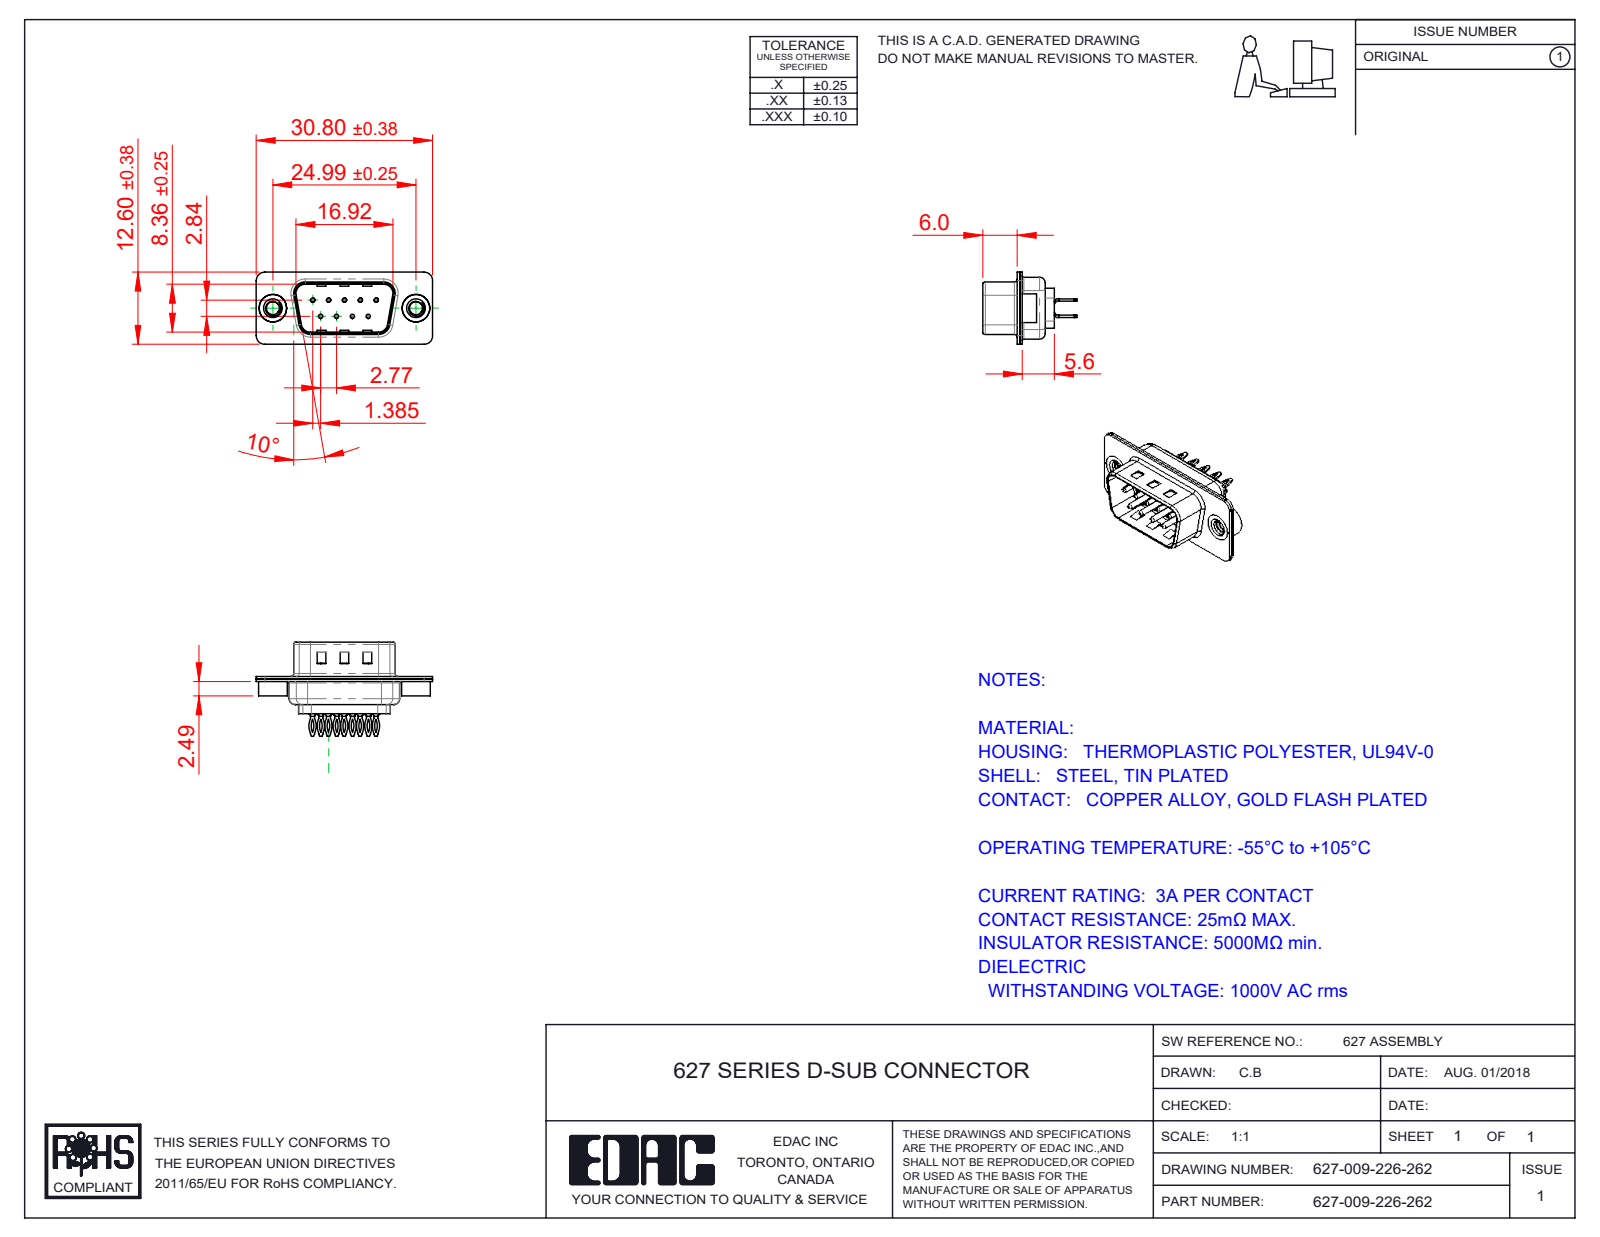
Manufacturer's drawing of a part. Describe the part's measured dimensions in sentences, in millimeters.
The part is named "627 Contact Row 2_26L; 627 Housing_09 LP; 627 Shell Front_09 Contacts; 627 Shell Rear_09 Contacts (+3 more)". Its 3-D file was written by "SolidWorks 2020 (CONFIG_CONTROL_DESIGN)". It is 14 solids with 984 faces: 287 planar, 406 cylindrical and 291 other. Overall it measures 30.8 by 16.45 by 12.6 millimeters. Its volume is 1 307 cubic millimeters and its surface area 3 895 square millimeters. Round holes: 9 of diameter 0.35, 9 of diameter 1.1, 9 of diameter 1.6, 2 of diameter 2.26, 2 of diameter 4, 2 of diameter 4.8. Round bosses or shafts: 9 of diameter 2, 9 of diameter 1.5, 9 of diameter 0.75, 2 of diameter 5, 2 of diameter 4.9. Partial cylindrical surfaces (rounded edges, fillets, slot ends): 18 of radius 1.5, 18 of radius 2.92, 18 of radius 3.33, 12 of radius 2, 8 of radius 0.5, 8 of radius 1.6, 4 of radius 0.25, 4 of radius 0.6. The main face-to-face distances are 0.4, 0.45, 0.9, 0.82, 9.58, 1.4, 8.76, 0.5, 1.5, 6.05. The hole center spacings are 3.16, 2.77, 5.54, 5.03, 5.04, 8.31, 7.48, 7.49.
